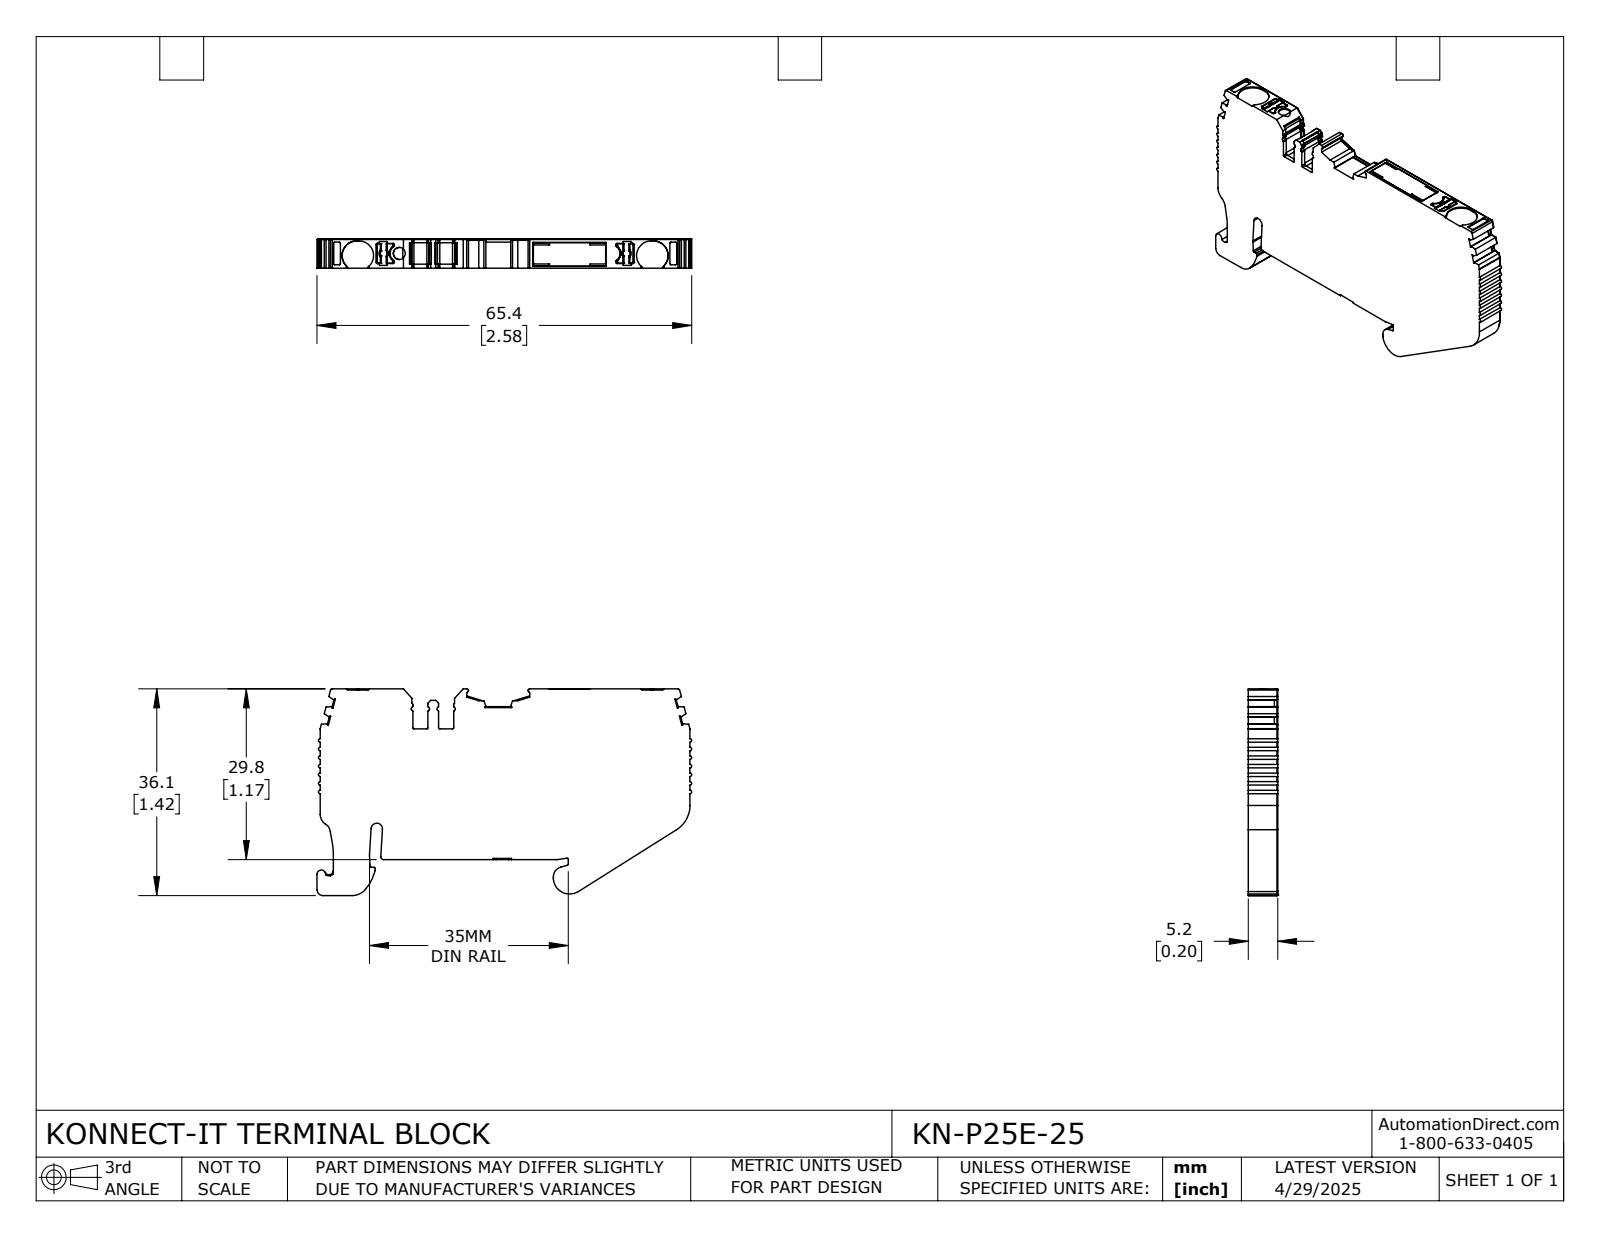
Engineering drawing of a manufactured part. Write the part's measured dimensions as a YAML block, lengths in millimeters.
part_name: "KN-P25E-25"
step_written_by: "SolidWorks 2024 (CONFIG_CONTROL_DESIGN)"
units: millimeters
bodies: {solids: 1, faces: 607, planar: 340, cylindrical: 230, other: 37}
overall_size: [65.4, 36.1, 5.2]
volume: 9590
surface_area: 5143
round_holes:
  - {diameter: 2.1, count: 1}
partial_cylinders:
  - {radius: 0.2, count: 54}
  - {radius: 0.3, count: 39}
  - {radius: 0.5, count: 18}
  - {radius: 0.1, count: 17}
  - {radius: 0.4, count: 9}
  - {radius: 0.2, count: 8}
  - {radius: 2.5, count: 4}
  - {radius: 1, count: 3}
face_to_face_distances: [5.2, 29.8, 29.6, 64.6, 4.5, 5, 6.2, 35.9, 2, 36.1]
